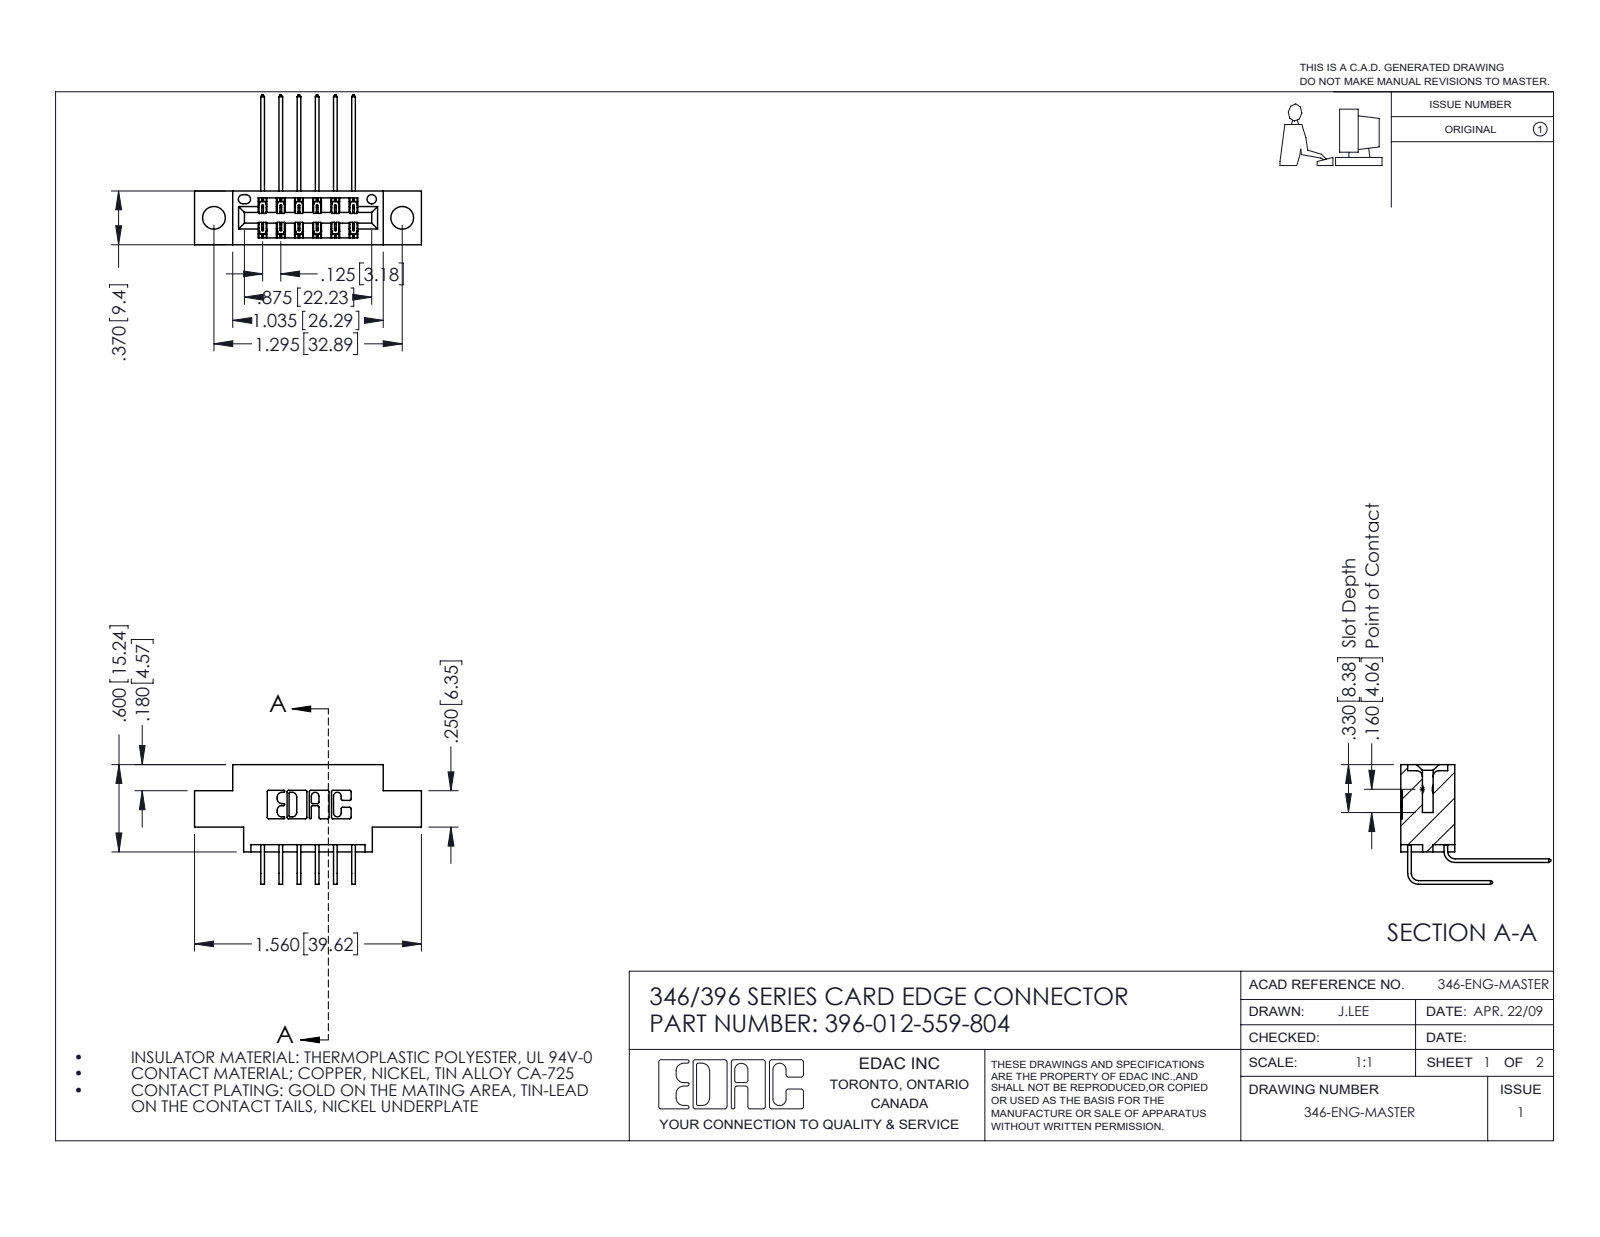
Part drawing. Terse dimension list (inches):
name: 345-292-001_559 Tail - 2; 346 Part_0.170 Offset - 0.156 Dia-TH; 396-012-559-804; 345-292-001_558 559 Tail - 1
written by: SolidWorks 2016 (CONFIG_CONTROL_DESIGN)
unit: in
bodies: 13 solids, 774 faces (524 planar, 250 cylindrical, 0 other)
size: 1.56 × 1.03 × 0.823
volume: 0.208 in³; area: 6.894 in²
holes: 2× ⌀0.156, 1× ⌀0.064
rounds: 22× R0.01, 18× R0.006, 6× R0.007, 6× R0.031, 3× R0.026, 2× R0.014, 2× R0.022, 2× R0.024
face distances: 0.25, 0.37, 0.048, 0.322, 0.025, 0.072, 0.125, 0.298, 0.148, 0.222
hole spacings: 0.246, 1.092, 1.295
